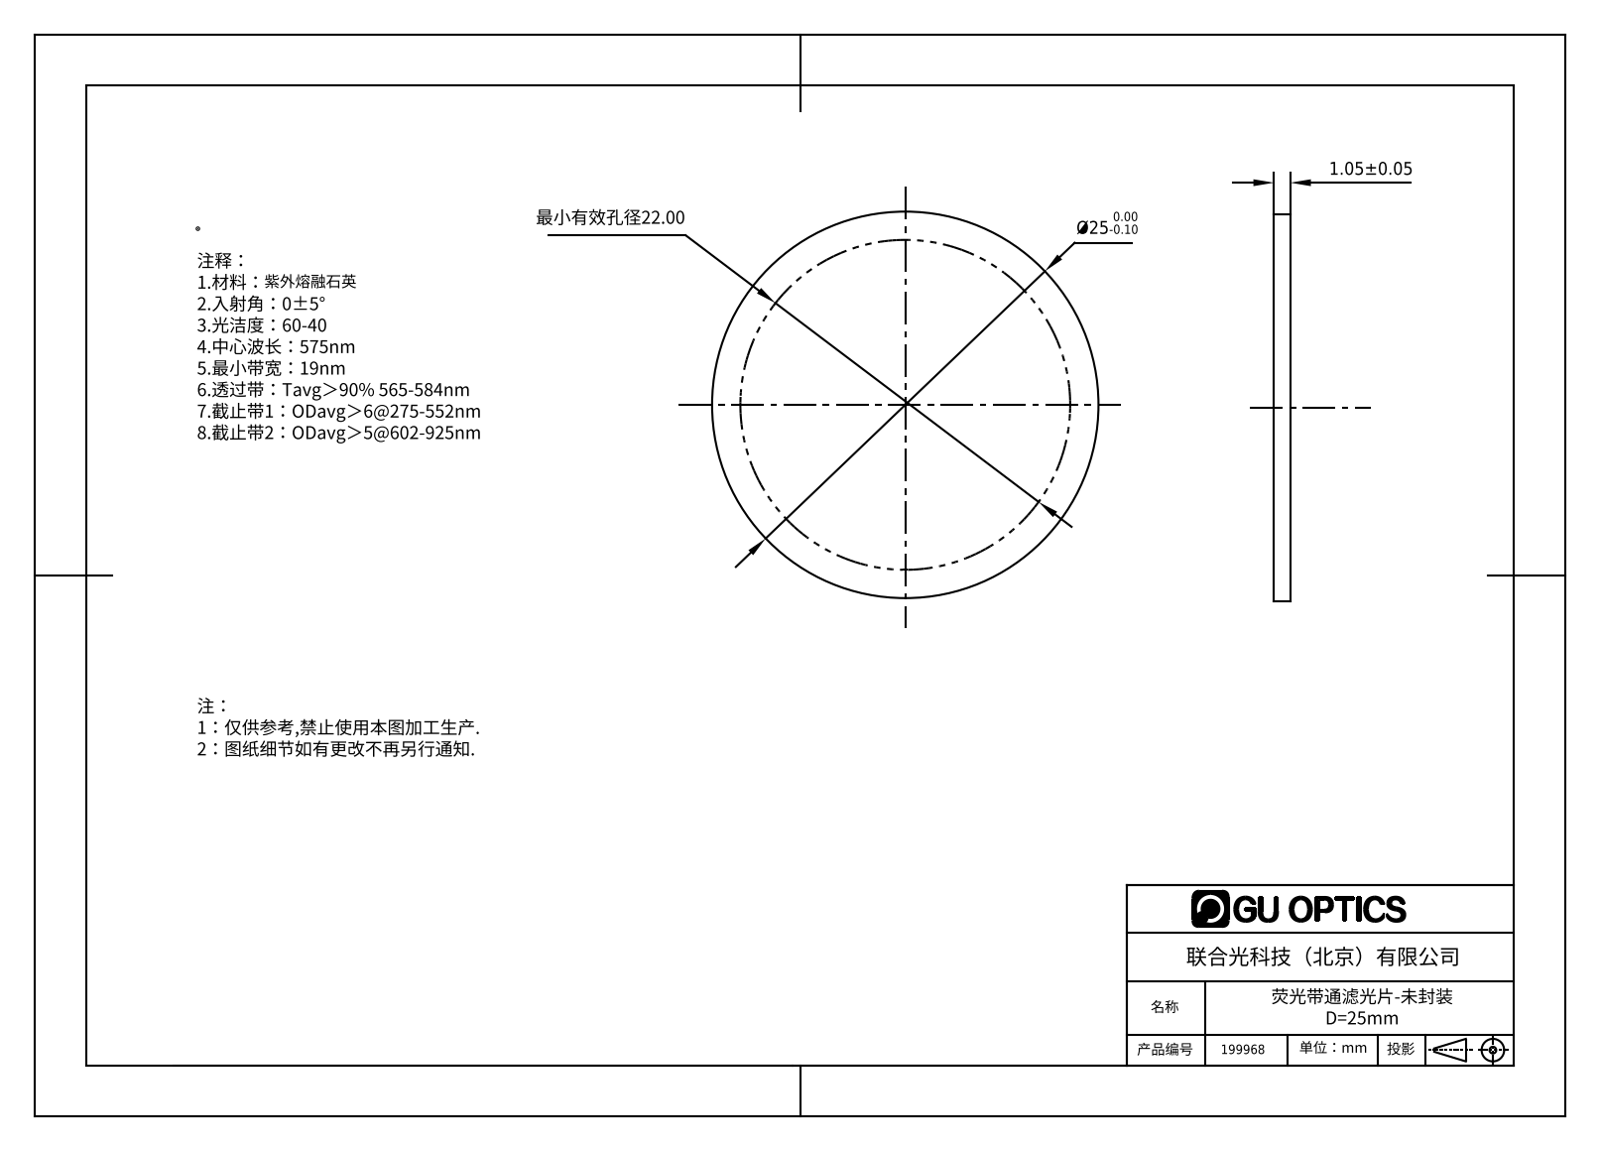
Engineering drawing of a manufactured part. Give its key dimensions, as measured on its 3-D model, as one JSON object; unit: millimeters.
{"part_name": "199968", "step_written_by": "SolidWorks 2016 (AUTOMOTIVE_DESIGN)", "units": "millimeters", "bodies": {"solids": 1, "faces": 4, "planar": 2, "cylindrical": 2, "other": 0}, "overall_size": [25, 25, 1.05], "volume_mm3": 515, "surface_area_mm2": 1064, "round_bosses_or_shafts": [[25, 1]], "face_to_face_distances": [1.05]}
